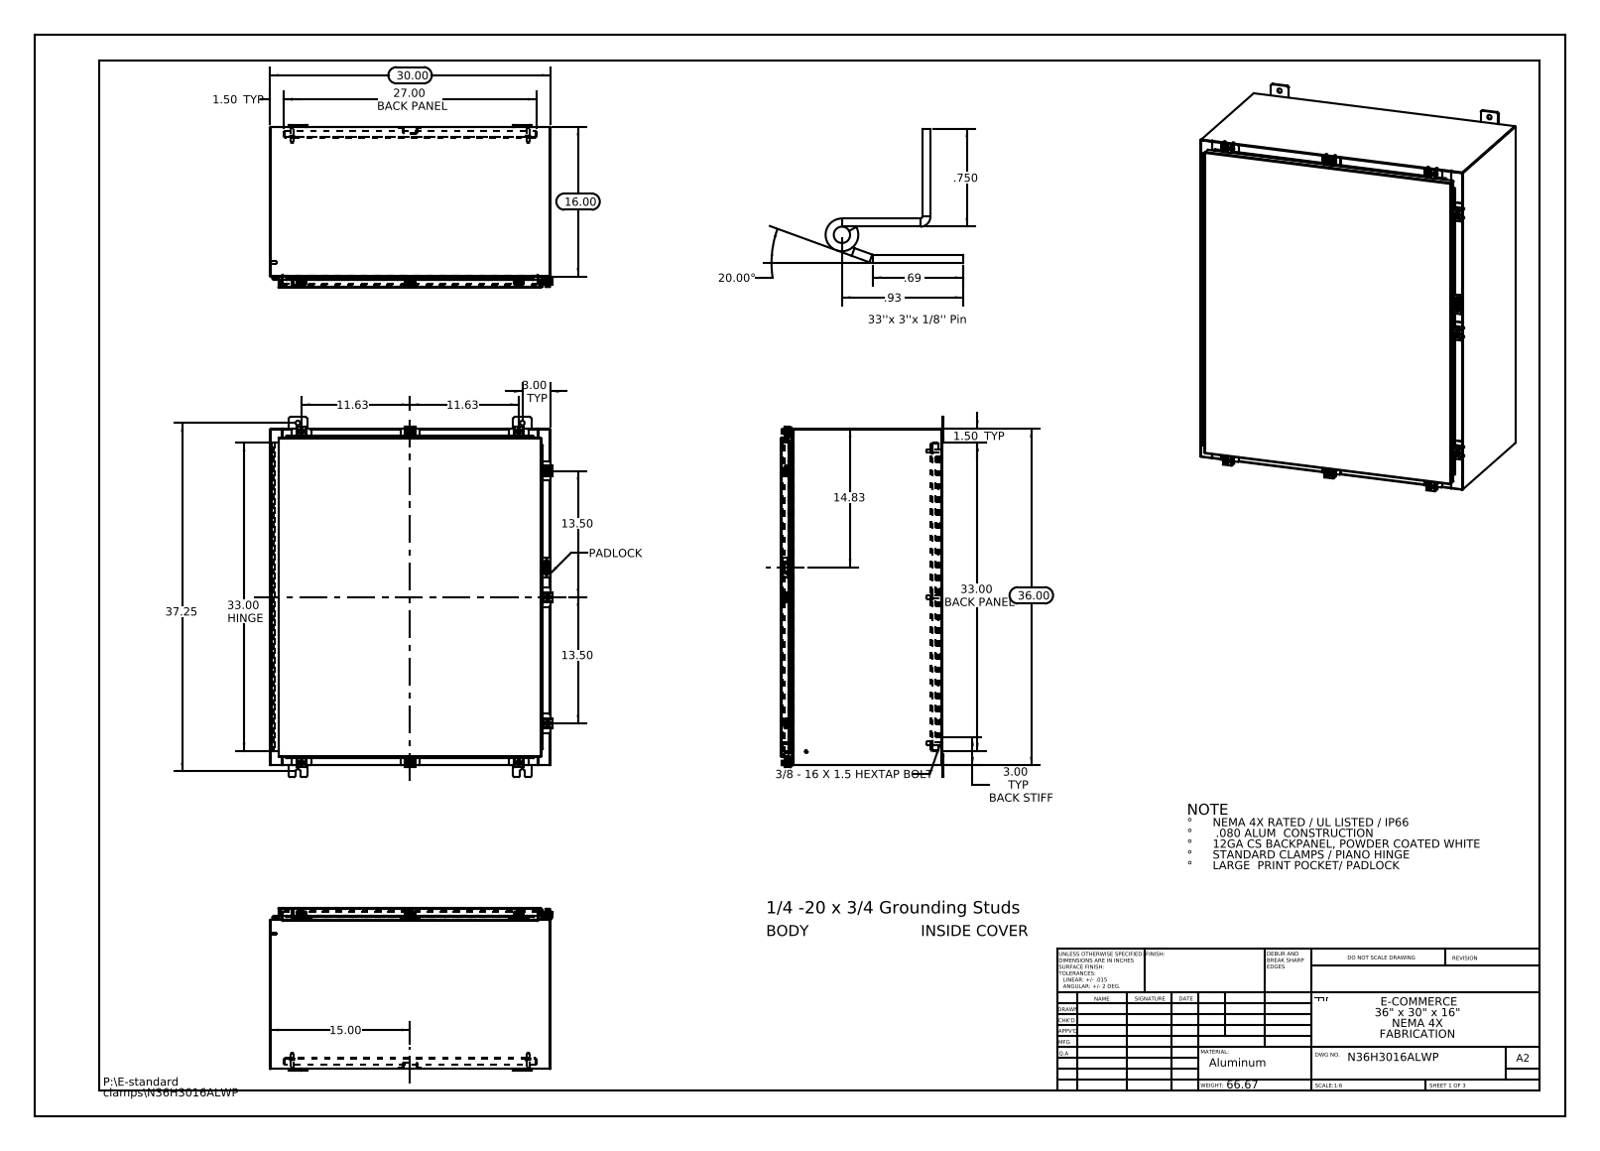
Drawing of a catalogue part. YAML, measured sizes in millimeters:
part_name: "N36H3016ALWP 125 Pin Hinge; N36H3016ALWP Clamp Top; N36H3016ALWP Enclosure Stiffener; N36H3016ALWP Hinge Cover Side (+8 more)"
step_written_by: "SolidWorks 2013 (CONFIG_CONTROL_DESIGN)"
units: millimeters
bodies: {solids: 67, faces: 2482, planar: 1294, cylindrical: 1036, other: 152}
overall_size: [977.9, 767.4, 441.7]
volume: 7554000
surface_area: 7501000
round_holes:
  - {diameter: 12.7, count: 10}
  - {diameter: 5.4, count: 9}
  - {diameter: 6.6, count: 9}
  - {diameter: 3.2, count: 2}
  - {diameter: 3.2, count: 1}
round_bosses_or_shafts:
  - {diameter: 6.4, count: 10}
  - {diameter: 12.7, count: 9}
  - {diameter: 10.1, count: 9}
  - {diameter: 15.9, count: 6}
  - {diameter: 9.5, count: 6}
  - {diameter: 8.4, count: 6}
  - {diameter: 8, count: 2}
  - {diameter: 6, count: 2}
partial_cylinders:
  - {radius: 1.5, count: 42}
  - {radius: 0.3, count: 31}
  - {radius: 2.2, count: 25}
  - {radius: 4.8, count: 24}
  - {radius: 3, count: 18}
  - {radius: 3.6, count: 18}
  - {radius: 1.3, count: 13}
  - {radius: 2, count: 12}
face_to_face_distances: [1.9, 435, 760.1, 433.1, 436.9, 2.6, 912.5, 25.4, 409.6, 27.3]
hole_center_spacings: [396.9, 451, 754.2, 847.5, 947.6, 641.4, 900.5, 47.2]
